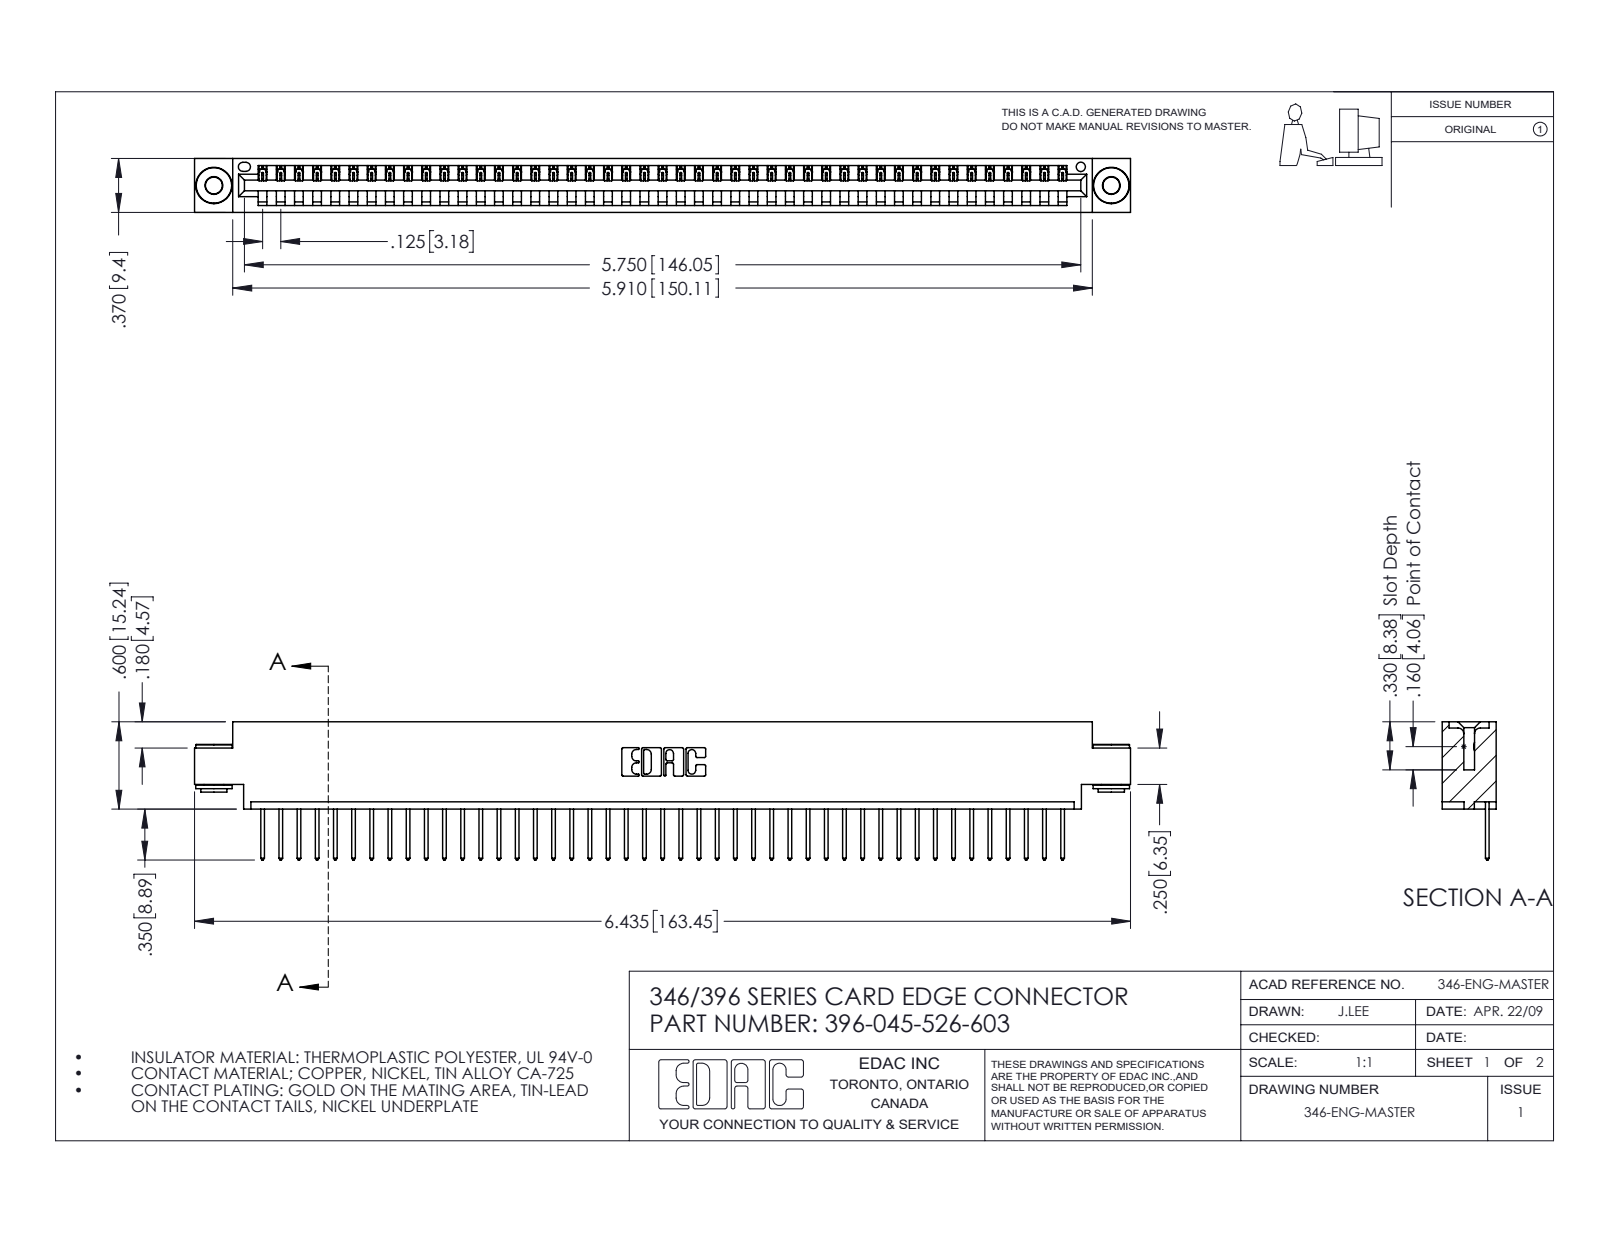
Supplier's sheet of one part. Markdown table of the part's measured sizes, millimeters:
| quantity | value |
| --- | --- |
| part name | 345-250-002_345-250-002-102; 396-045-526-603; 346 Part_0.170 Offset - 0.156 Dia-TH; 345-292-001_345-293-126 |
| STEP written by | SolidWorks 2016 (CONFIG_CONTROL_DESIGN) |
| units | millimeters |
| bodies | 48 solids, 2774 faces (1890 planar, 876 cylindrical, 8 other) |
| overall size | 163.4 × 24.1 × 9.4 |
| volume | 15 500 mm³ |
| surface area | 19 740 mm² |
| round holes (diameter × count) | 2.9 × 2, 4 × 2, 1.6 × 1 |
| round bosses / shafts (diameter × count) | 6.4 × 2, 4.6 × 2, 3.5 × 2 |
| partial cylindrical surfaces (radius × count) | 0.2 × 90, 0.3 × 90, 0.3 × 22, 0.2 × 6, 0.8 × 6, 0.7 × 3, 0.8 × 2, 1 × 2 |
| main face-to-face distances | 1.2, 8.2, 9.4, 6.4, 0.6, 1.8, 7.6, 3.8, 5.6, 2.5 |
| hole center spacings | 6.2, 151.4, 156.7 |
